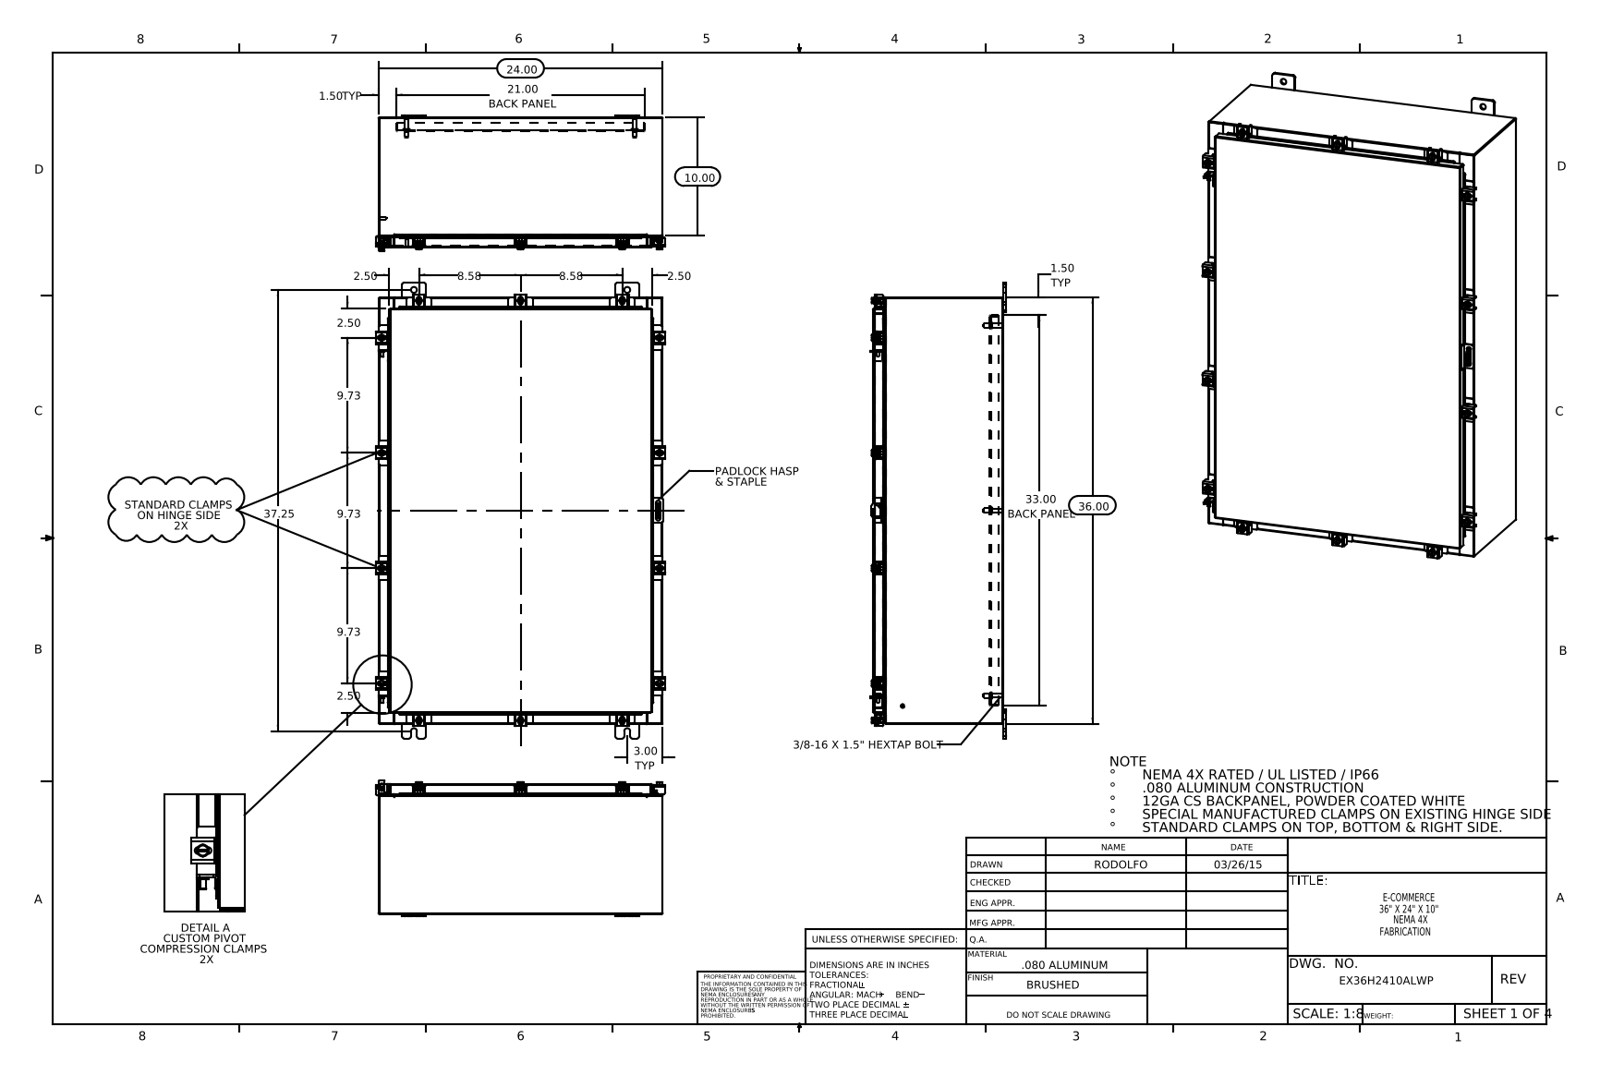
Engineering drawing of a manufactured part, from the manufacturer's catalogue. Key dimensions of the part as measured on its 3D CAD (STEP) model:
Part name (STEP PRODUCT): EX36H2410ALWP Body; N-WMT04X30402202210-00 22104005_DEFAULT; EX36H2410ALWP Cover; EX36H2410ALWP Top (+8 more)
STEP written by: SolidWorks 2014 (CONFIG_CONTROL_DESIGN)
Units: inches
Bodies: 93 solids, 2322 faces (1221 planar, 905 cylindrical, 196 other)
Overall size (bounding box): 38.5 × 24.421 × 11.453
Volume: 327.4 in³ · Surface area: 8 148 in²
Round holes (diameter × count): ⌀0.213 ×14, ⌀0.26 ×14, ⌀0.5 ×10, ⌀0.125 ×1, ⌀0.25 ×1
Round bosses / shafts (diameter × count): ⌀0.5 ×14, ⌀0.25 ×14, ⌀0.399 ×12, ⌀0.625 ×6, ⌀0.375 ×6, ⌀0.33 ×6, ⌀0.315 ×2, ⌀0.236 ×2
Partial cylindrical surfaces — rounded edges, fillets, slot ends (radius × count): R0.06 ×62, R0.141 ×28, R0.013 ×26, R0.12 ×26, R0.19 ×24, R0.088 ×22, R0.09 ×20, R0.05 ×19
Main face-to-face distances: 0.075, 10.9, 10.975, 10.826, 0.104, 23.925, 1, 1.075, 9.826, 9.9
Hole centre spacings: 25.389, 2.347, 4.44, 5.299, 9.73, 10.964, 13.241, 14.744
